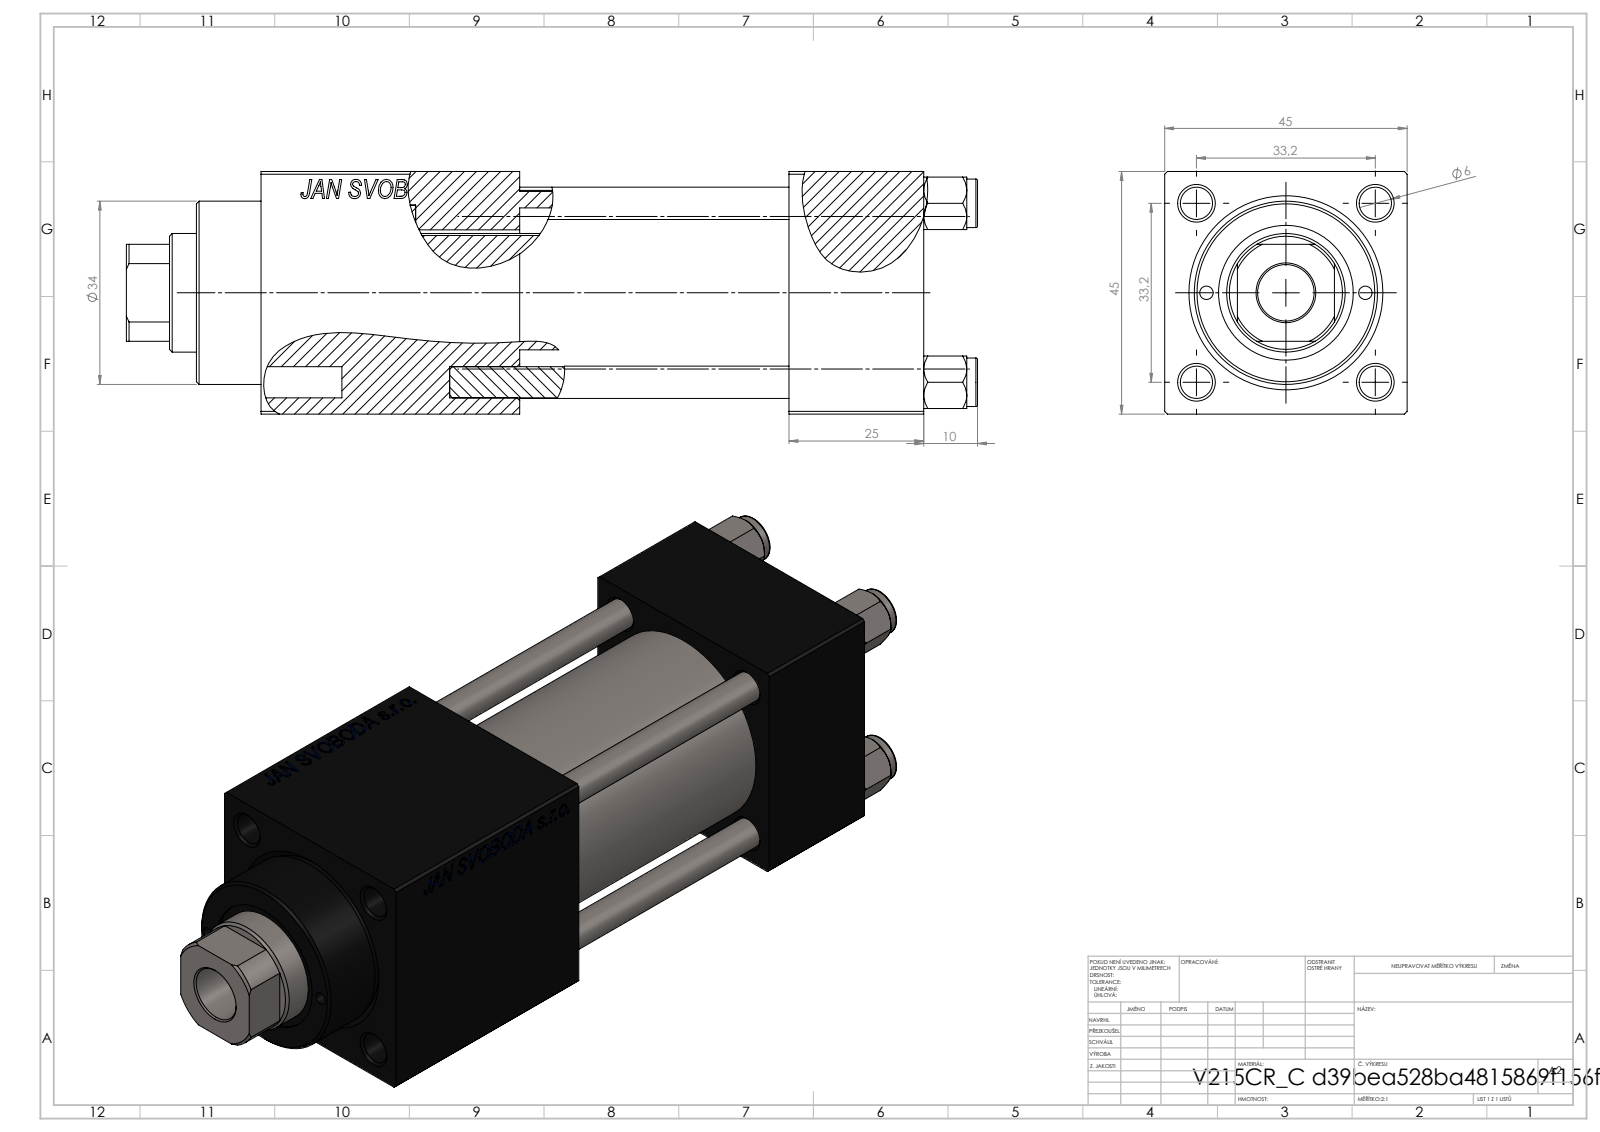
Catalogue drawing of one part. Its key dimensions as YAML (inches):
part_name: "V215_VC_A; V215CR_VCP_C; V215CR_C_Body; NUT_M5_C (+1 more)"
step_written_by: "SolidWorks 2019 (CONFIG_CONTROL_DESIGN)"
units: inches
bodies: {solids: 11, faces: 1154, planar: 527, cylindrical: 91, other: 536}
overall_size: [6.22, 1.772, 1.772]
volume: 12.79
surface_area: 110.9
round_holes:
  - {diameter: 0.236, count: 4}
  - {diameter: 0.098, count: 2}
  - {diameter: 0.276, count: 2}
  - {diameter: 0.518, count: 2}
  - {diameter: 0.787, count: 2}
  - {diameter: 0.413, count: 1}
  - {diameter: 0.866, count: 1}
  - {diameter: 0.945, count: 1}
  - {diameter: 0.984, count: 1}
  - {diameter: 1.26, count: 1}
  - {diameter: 1.299, count: 1}
round_bosses_or_shafts:
  - {diameter: 0.354, count: 4}
  - {diameter: 1.496, count: 1}
  - {diameter: 1.339, count: 1}
partial_cylinders:
  - {radius: 0.413, count: 1}
face_to_face_distances: [1.772, 0.984, 1.969, 4.843, 2.953, 3.858, 1.89, 3.713, 2.728, 0.76]
hole_center_spacings: [0.657, 0.924, 1.307, 1.396, 0.581, 1.848, 1.161, 2.972]
